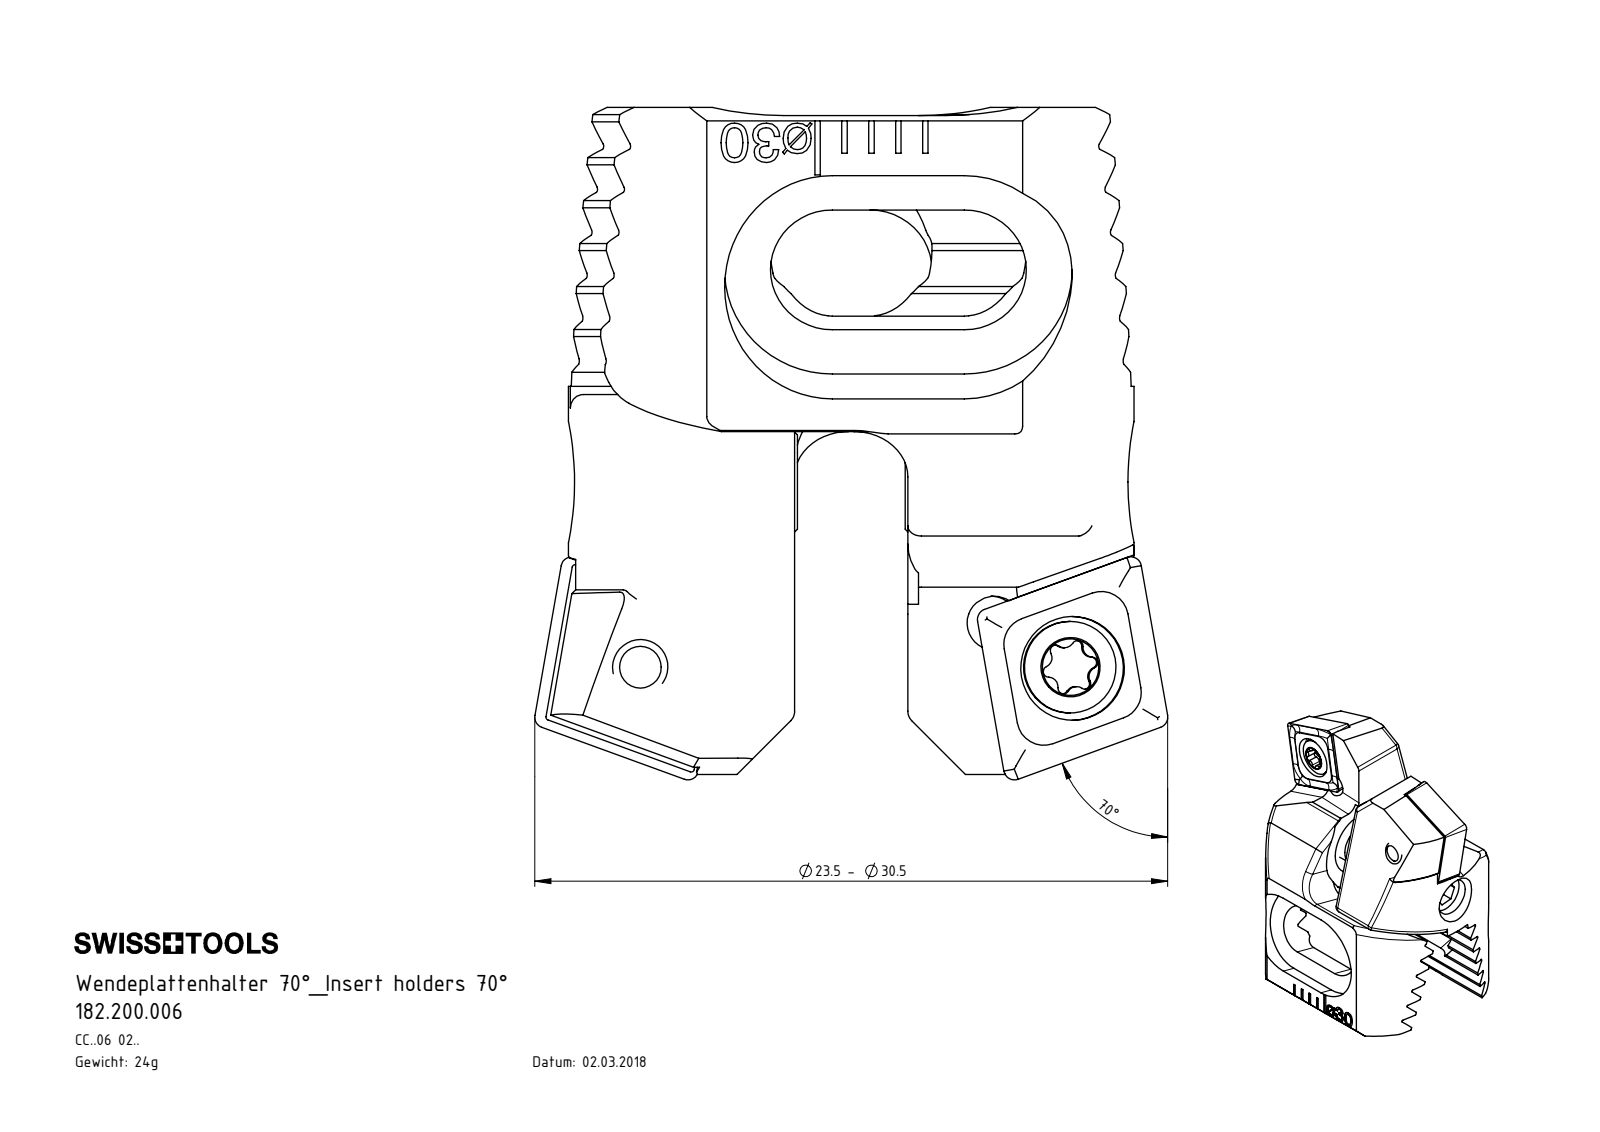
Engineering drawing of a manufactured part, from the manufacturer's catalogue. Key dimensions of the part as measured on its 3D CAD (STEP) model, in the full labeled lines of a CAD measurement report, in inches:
Part name (STEP PRODUCT): Z20-ER3.001.007_A; 182.200.006; CCMT060204; Z20-xxx.001.015_D_70ø (+1 more)
STEP written by: SolidWorks 2017 (CONFIG_CONTROL_DESIGN)
Units: inches
Bodies: 8 solids, 608 faces (266 planar, 136 cylindrical, 206 other)
Overall size (bounding box): 0.982 × 0.925 × 0.638
Volume: 0.179 in³ · Surface area: 5.262 in²
Round holes (diameter × count): ⌀0.063 ×2, ⌀0.079 ×2, ⌀0.081 ×2, ⌀0.11 ×2, ⌀0.152 ×2, ⌀0.138 ×1, ⌀0.358 ×1
Round bosses / shafts (diameter × count): ⌀0.134 ×2, ⌀0.098 ×2, ⌀0.157 ×1
Partial cylindrical surfaces — rounded edges, fillets, slot ends (radius × count): R0.02 ×16, R0.005 ×12, R0.008 ×12, R0.014 ×10, R0.039 ×6, R0.079 ×4, R0.091 ×4, R0.157 ×4
Main face-to-face distances: 0.056, 0.113, 0.169, 0.149, 0.016, 0.181, 0.225, 0.225, 0.117, 0.266
Hole centre spacings: 0.129, 0.132, 0.217, 0.532, 0.535, 0.643, 0.416, 0.418
